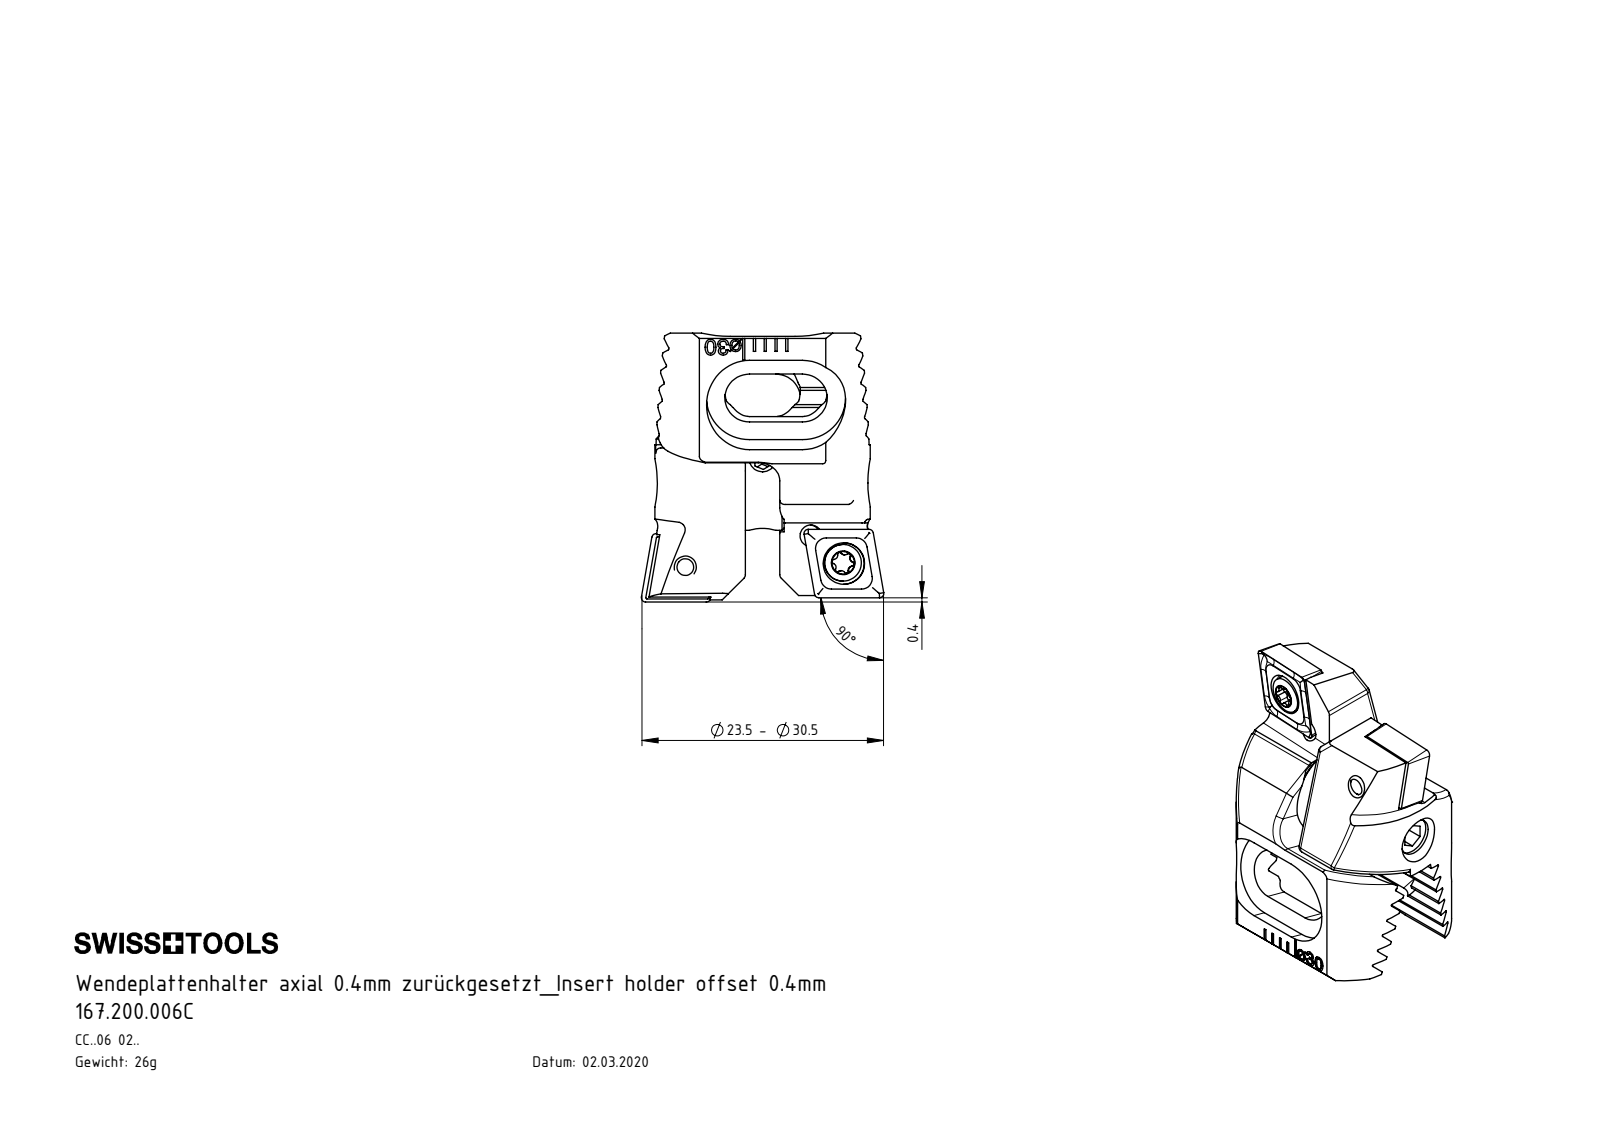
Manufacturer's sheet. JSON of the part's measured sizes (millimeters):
{"part_name": "167.200.006C; Z20-ER3.000.018; Z20-xxx.001.015_D_versetzt; Z20-xxx.001.015_D (+5 more)", "step_written_by": "SolidWorks 2022 (AUTOMOTIVE_DESIGN)", "units": "millimeters", "bodies": {"solids": 11, "faces": 677, "planar": 282, "cylindrical": 159, "other": 236}, "overall_size": [24.95, 22.5, 16.2], "volume_mm3": 3145, "surface_area_mm2": 3796, "round_holes": [[1.6, 4], [2.5, 3], [2, 2], [2.05, 2], [2.8, 2], [3.85, 2], [3.5, 1], [9.1, 1]], "round_bosses_or_shafts": [[3, 4], [3.4, 2], [2.5, 2], [8.8, 1], [4, 1]], "partial_cylinders_radius": [[0.5, 16], [0.12, 12], [0.21, 12], [0.36, 8], [0.36, 4], [2, 4], [2.3, 4], [4, 4]], "face_to_face_distances": [1.43, 2.86, 4.29, 0.4, 3.79, 5.71, 5.72, 3.6, 4, 2.97], "hole_center_spacings": [2.5, 3.91, 4.01, 5.5, 5, 6.05, 7.43, 8.92]}
